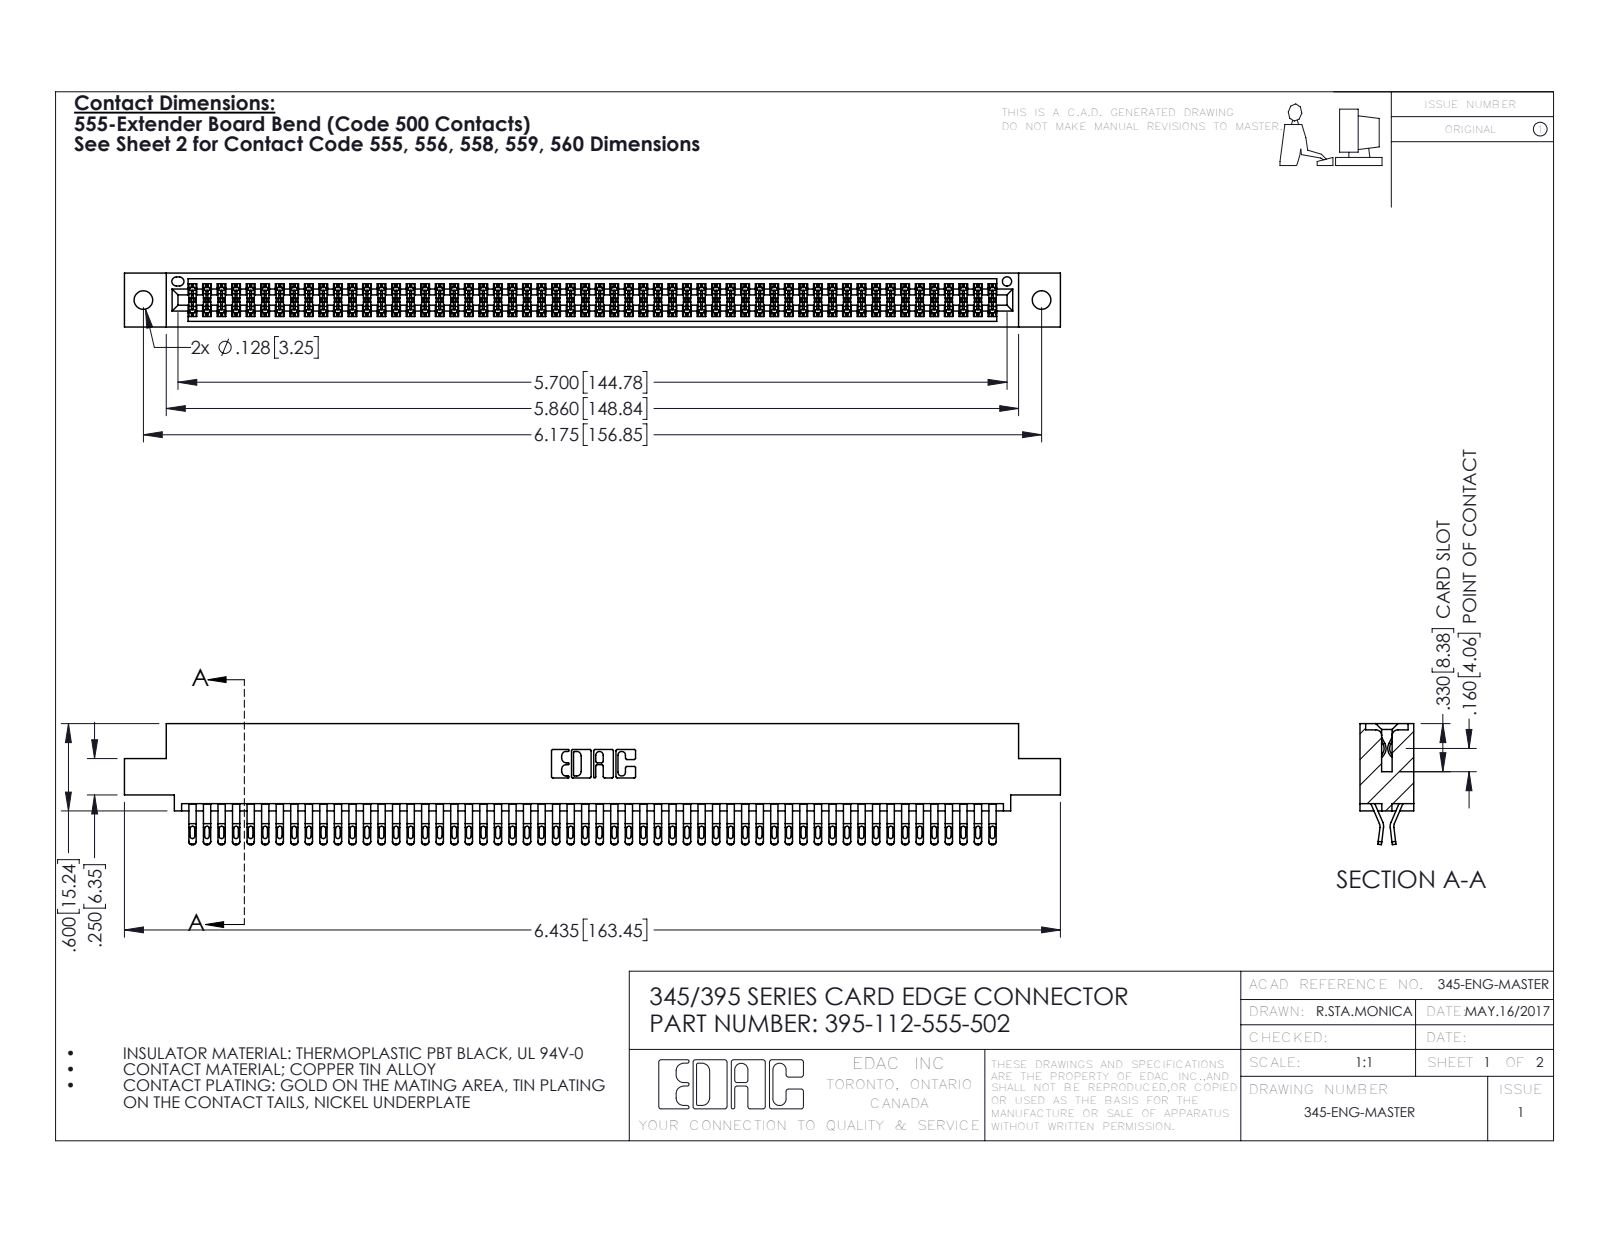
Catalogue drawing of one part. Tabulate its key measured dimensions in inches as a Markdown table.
| quantity | value |
| --- | --- |
| part name | 395-112-555-502; 345-292-001_555 Tail; 345 Part_0.110 Offset - 0.128 Dia |
| STEP written by | SolidWorks 2016 (CONFIG_CONTROL_DESIGN) |
| units | inches |
| bodies | 113 solids, 6402 faces (3556 planar, 2846 cylindrical, 0 other) |
| overall size | 6.435 × 0.832 × 0.37 |
| volume | 0.99 in³ |
| surface area | 39.06 in² |
| round holes (diameter × count) | 0.128 × 2, 0.064 × 1 |
| partial cylindrical surfaces (radius × count) | 0.016 × 280, 0.02 × 224, 0.006 × 168, 0.01 × 22, 0.007 × 6, 0.031 × 6, 0.026 × 3, 0.01 × 2 |
| main face-to-face distances | 0.298, 0.072, 0.025, 0.37, 0.2, 0.098, 0.272, 0.225, 0.175, 0.149 |
| hole center spacings | 0.27, 5.939, 6.175 |
